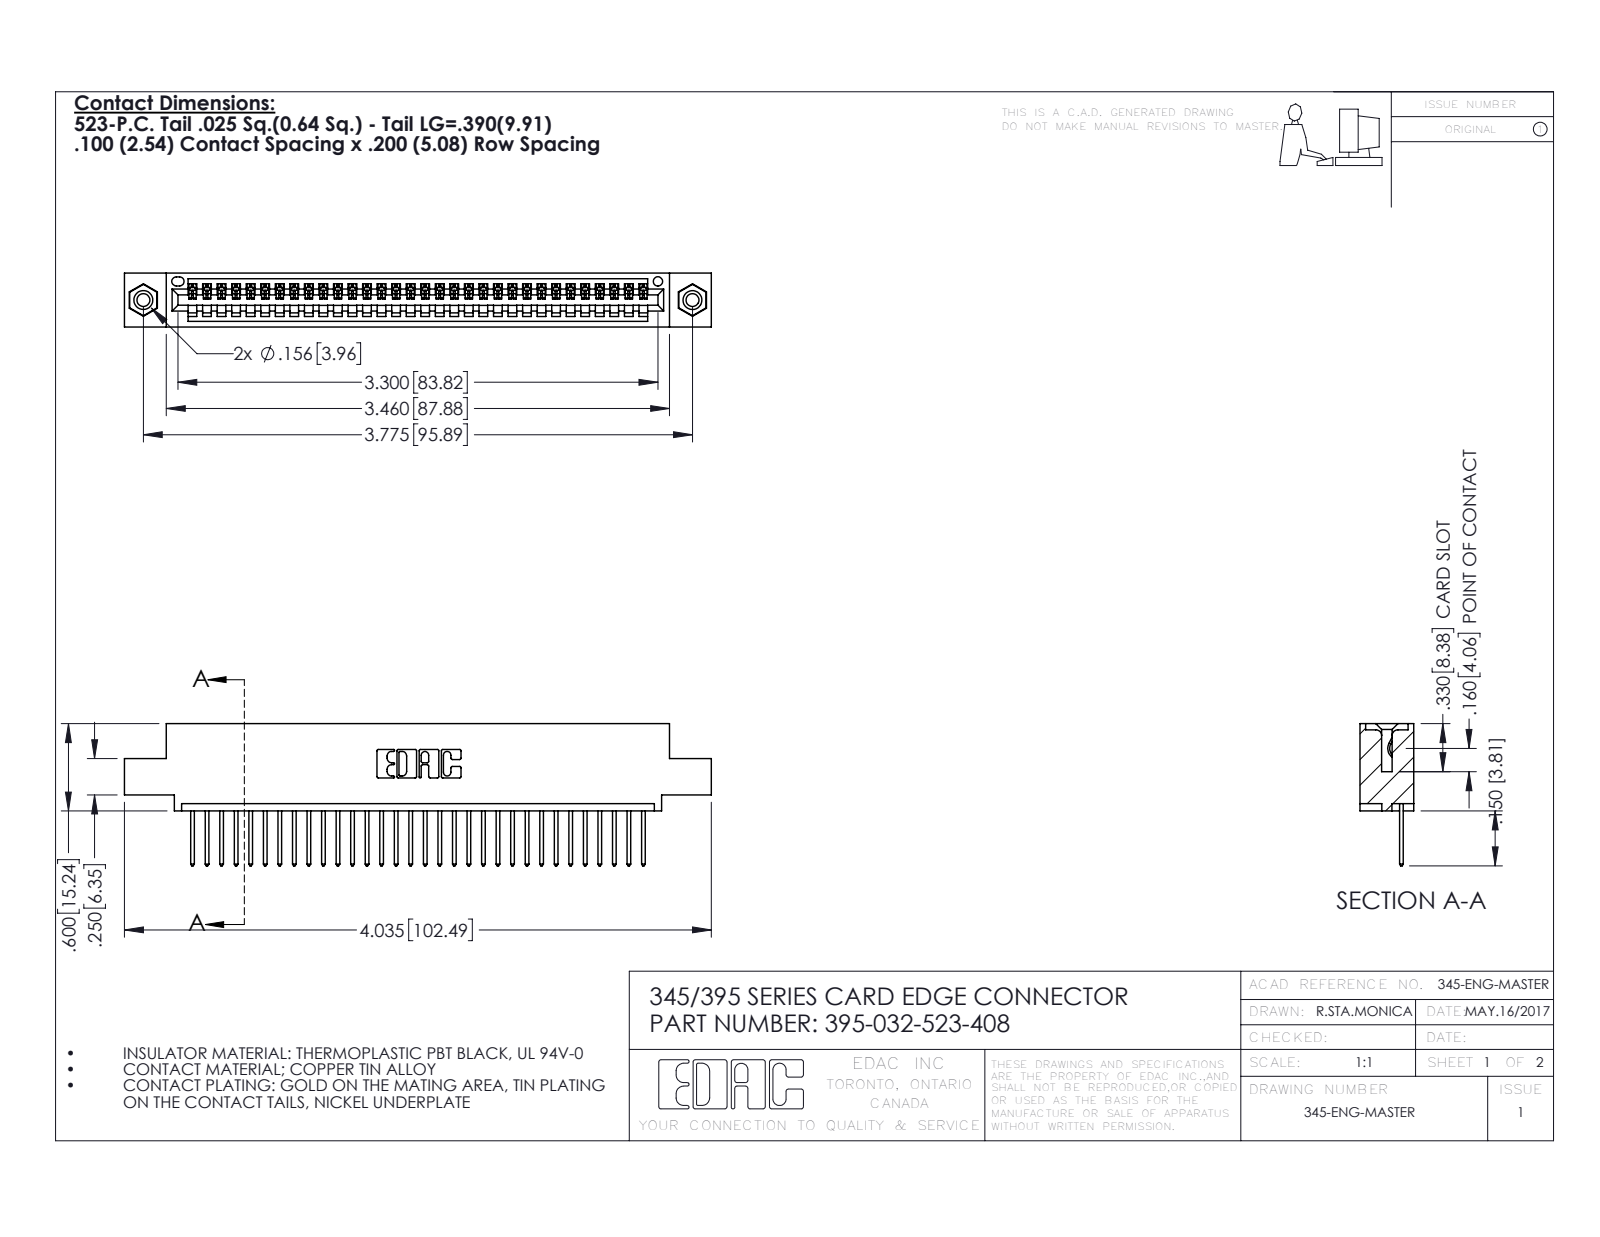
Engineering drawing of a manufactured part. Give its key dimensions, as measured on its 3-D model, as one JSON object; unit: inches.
{"part_name": "345-292-001_345-293-123; 345 Part_0.110 Offset - 0.156 Dia-TI; 395-032-523-408; 345-250-001_345-250-003-102", "step_written_by": "SolidWorks 2016 (CONFIG_CONTROL_DESIGN)", "units": "inches", "bodies": {"solids": 35, "faces": 2046, "planar": 1396, "cylindrical": 634, "other": 16}, "overall_size": [4.035, 0.977, 0.37], "volume_in3": 0.583, "surface_area_in2": 19.69, "round_holes": [[0.089, 2], [0.125, 2], [0.156, 2], [0.064, 1]], "round_bosses_or_shafts": [[0.155, 2]], "partial_cylinders_radius": [[0.006, 64], [0.01, 64], [0.01, 22], [0.007, 6], [0.031, 6], [0.026, 3], [0.031, 2], [0.04, 2]], "face_to_face_distances": [0.072, 0.298, 0.37, 0.2, 0.098, 0.272, 0.025, 0.225, 0.149, 0.072], "hole_center_spacings": [0.27, 3.54, 3.775]}
